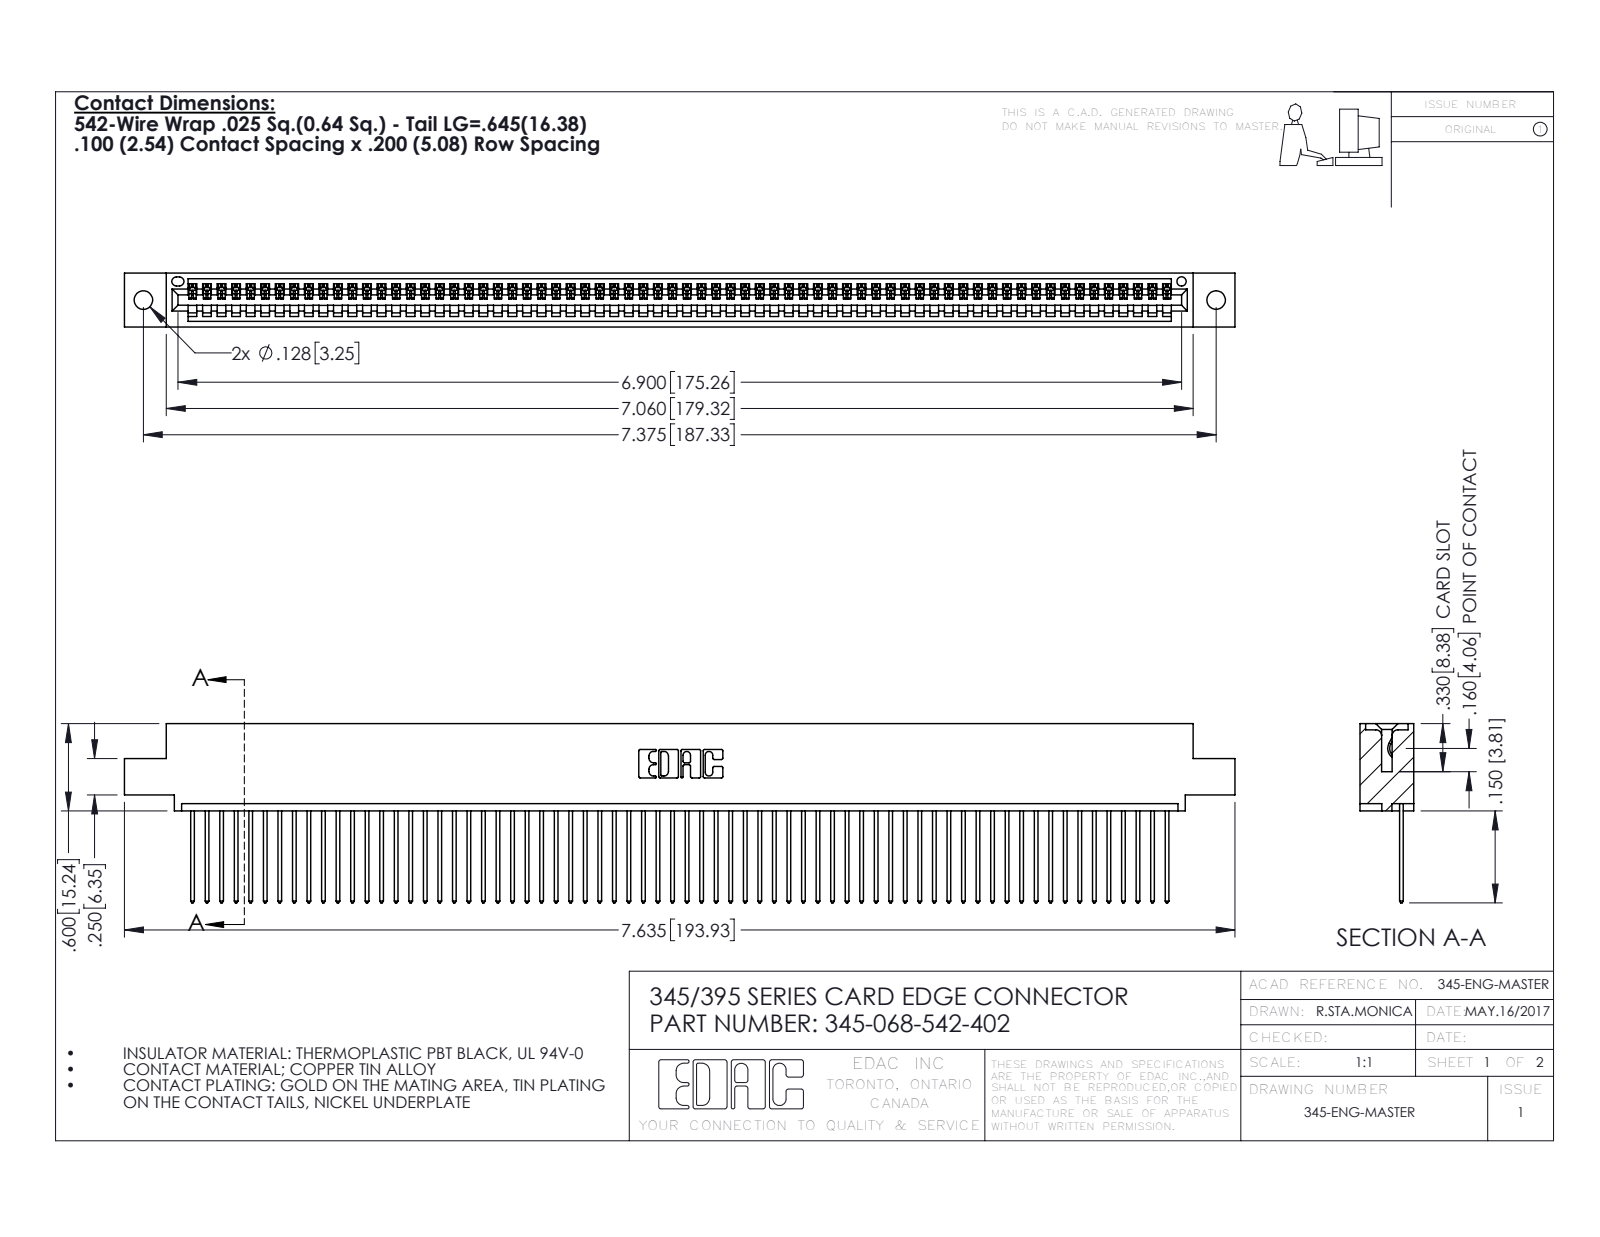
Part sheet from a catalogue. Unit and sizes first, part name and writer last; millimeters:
Units: millimetres
Overall size (bounding box): 193.9 × 31.3 × 9.4
Round holes (diameter × count): ⌀3.3 ×2, ⌀1.6 ×1
Partial cylindrical surfaces — rounded edges, fillets, slot ends (radius × count): R0.2 ×136, R0.3 ×136, R0.3 ×22, R0.2 ×6, R0.8 ×6, R0.7 ×3, R0.8 ×2, R1 ×2
Main face-to-face distances: 1.8, 7.6, 2.5, 6.9, 0.6, 9.4, 5.1, 5.7, 3.8, 1.8
Hole centre spacings: 6.9, 181.3, 187.3
Volume: 18 680 mm³ · Surface area: 25 940 mm²
Bodies: 69 solids, 4074 faces (2804 planar, 1270 cylindrical, 0 other)
Part name (STEP PRODUCT): 345 Part_0.110 Offset - 0.128 Dia; 345-292-001_345-293-142; 345-068-542-402
STEP written by: SolidWorks 2016 (CONFIG_CONTROL_DESIGN)
